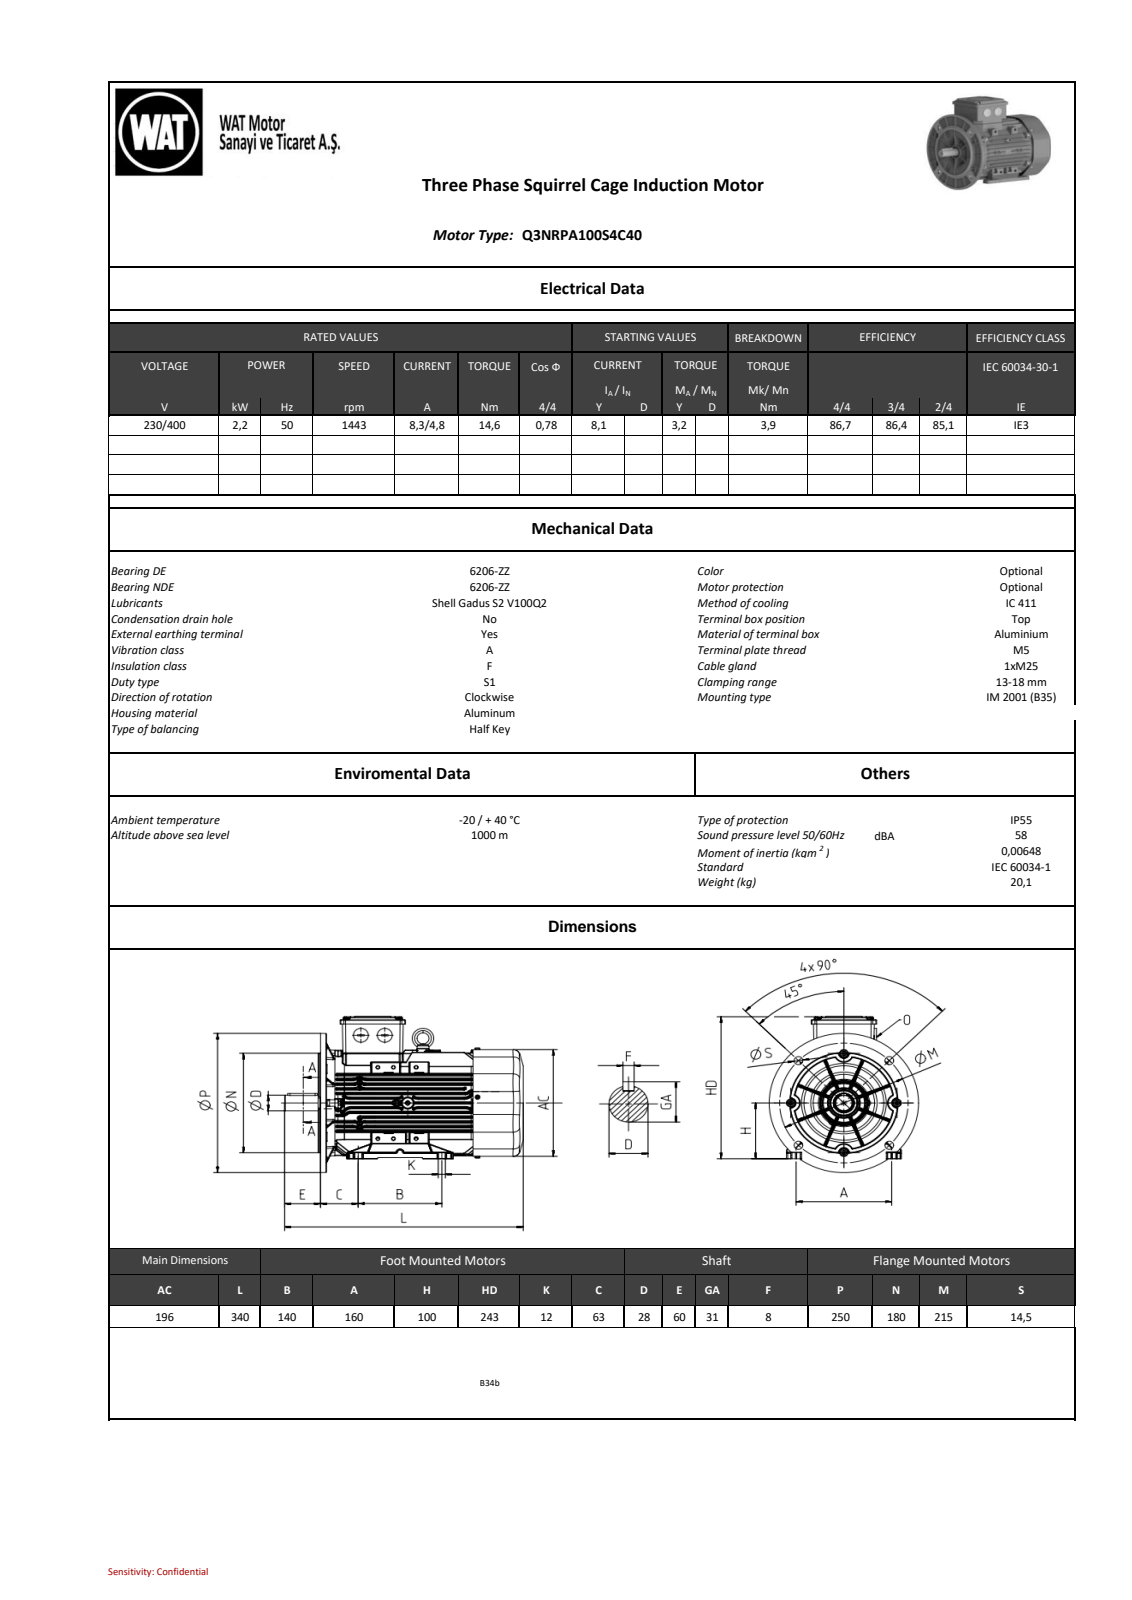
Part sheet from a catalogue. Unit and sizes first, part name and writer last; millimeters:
Units: millimetres
Overall size (bounding box): 340 × 254.96 × 248.92
Round holes (diameter × count): ⌀5 ×6, ⌀6.5 ×6, ⌀2 ×2, ⌀2.5 ×2, ⌀3 ×2, ⌀12 ×2, ⌀25 ×2, ⌀4 ×1, ⌀8.5 ×1, ⌀10.5 ×1, ⌀28.6 ×1, ⌀32.94 ×1
Round bosses / shafts (diameter × count): ⌀8 ×7, ⌀4 ×7, ⌀11.8 ×6, ⌀10 ×6, ⌀6 ×6, ⌀35 ×2, ⌀27.8 ×2, ⌀25.25 ×2
Partial cylindrical surfaces — rounded edges, fillets, slot ends (radius × count): R0.5 ×1716, R0.75 ×600, R0.8 ×499, R1 ×241, R0.25 ×144, R2 ×111, R4 ×102, R1.5 ×96
Main face-to-face distances: 0.8, 6, 2, 7.2, 13.2, 41, 239, 3, 266, 273.2
Hole centre spacings: 92, 39, 96.14, 156.89, 184, 12.13, 14.13, 17.07
Bodies: 0 solids, 15957 faces (3368 planar, 5391 cylindrical, 7198 other)
Part name (STEP PRODUCT): C90127E0127Fj7eb
STEP written by: SIEMENS PLM Software NX 11.0 (AUTOMOTIVE_DESIGN)
